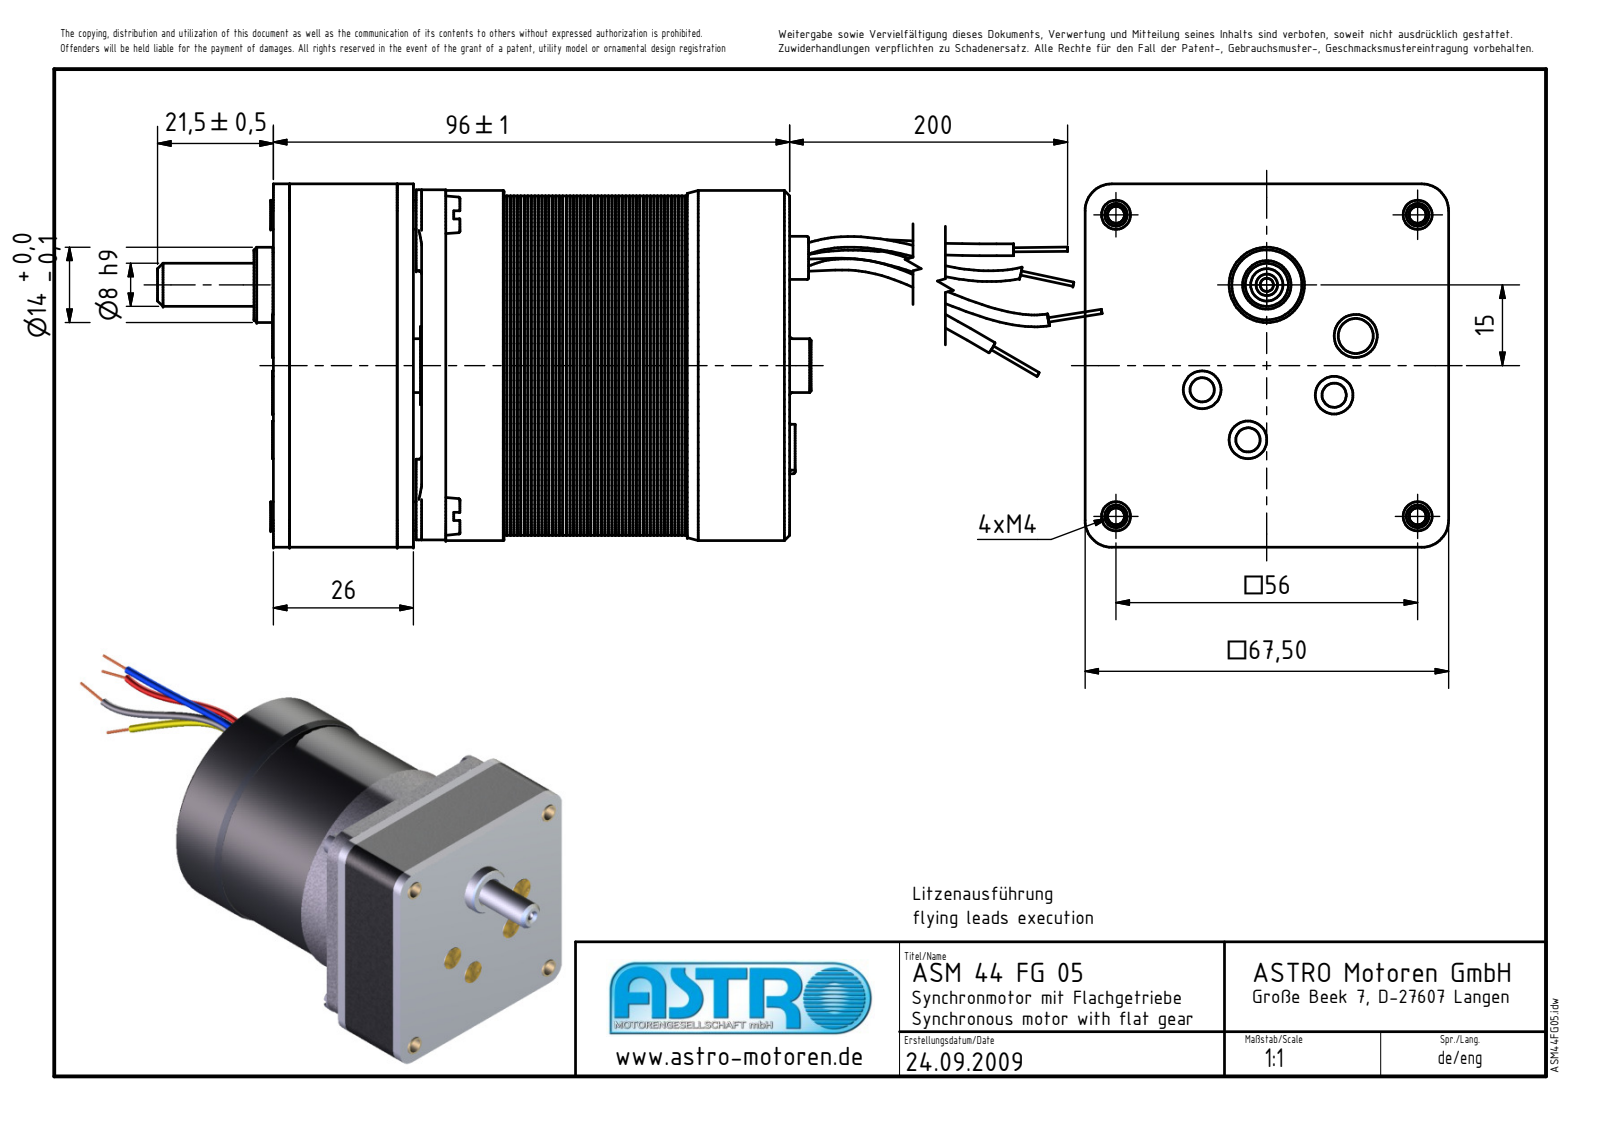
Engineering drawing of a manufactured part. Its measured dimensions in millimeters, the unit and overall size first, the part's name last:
Units: millimetres
Overall size (bounding box): 193.98 × 67.5 × 67.5
Round holes (diameter × count): ⌀3.24 ×9, ⌀1.6 ×8, ⌀4.1 ×8, ⌀4.2 ×8, ⌀5 ×5, ⌀4.4 ×4, ⌀8.5 ×4, ⌀4.5 ×3, ⌀2.46 ×2, ⌀5.5 ×1, ⌀6 ×1, ⌀6.5 ×1
Round bosses / shafts (diameter × count): ⌀4 ×8, ⌀8 ×6, ⌀15 ×4, ⌀5.39 ×4, ⌀4.84 ×4, ⌀3.62 ×4, ⌀3.57 ×4, ⌀7 ×3
Partial cylindrical surfaces — rounded edges, fillets, slot ends (radius × count): R0.5 ×32, R2.25 ×8, R3.5 ×8, R3 ×4, R5 ×4, R5.26 ×4, R6 ×1, R11 ×1
Main face-to-face distances: 1.3, 0.65, 1.95, 2.6, 3.25, 3.9, 3, 4.55, 5.2, 23
Hole centre spacings: 27, 31.46, 55.42, 47, 38.18, 49.89, 11.29, 54
Volume: 141 379 mm³ · Surface area: 248 723 mm²
Bodies: 91 solids, 9199 faces (3383 planar, 5668 cylindrical, 148 other)
Part name (STEP PRODUCT): ASM44FG05; 500-ASM44; Motorflansch-A-Metall; MotorflanschB2 (+8 more)
STEP written by: Autodesk Inventor 2017 (AUTOMOTIVE_DESIGN)
